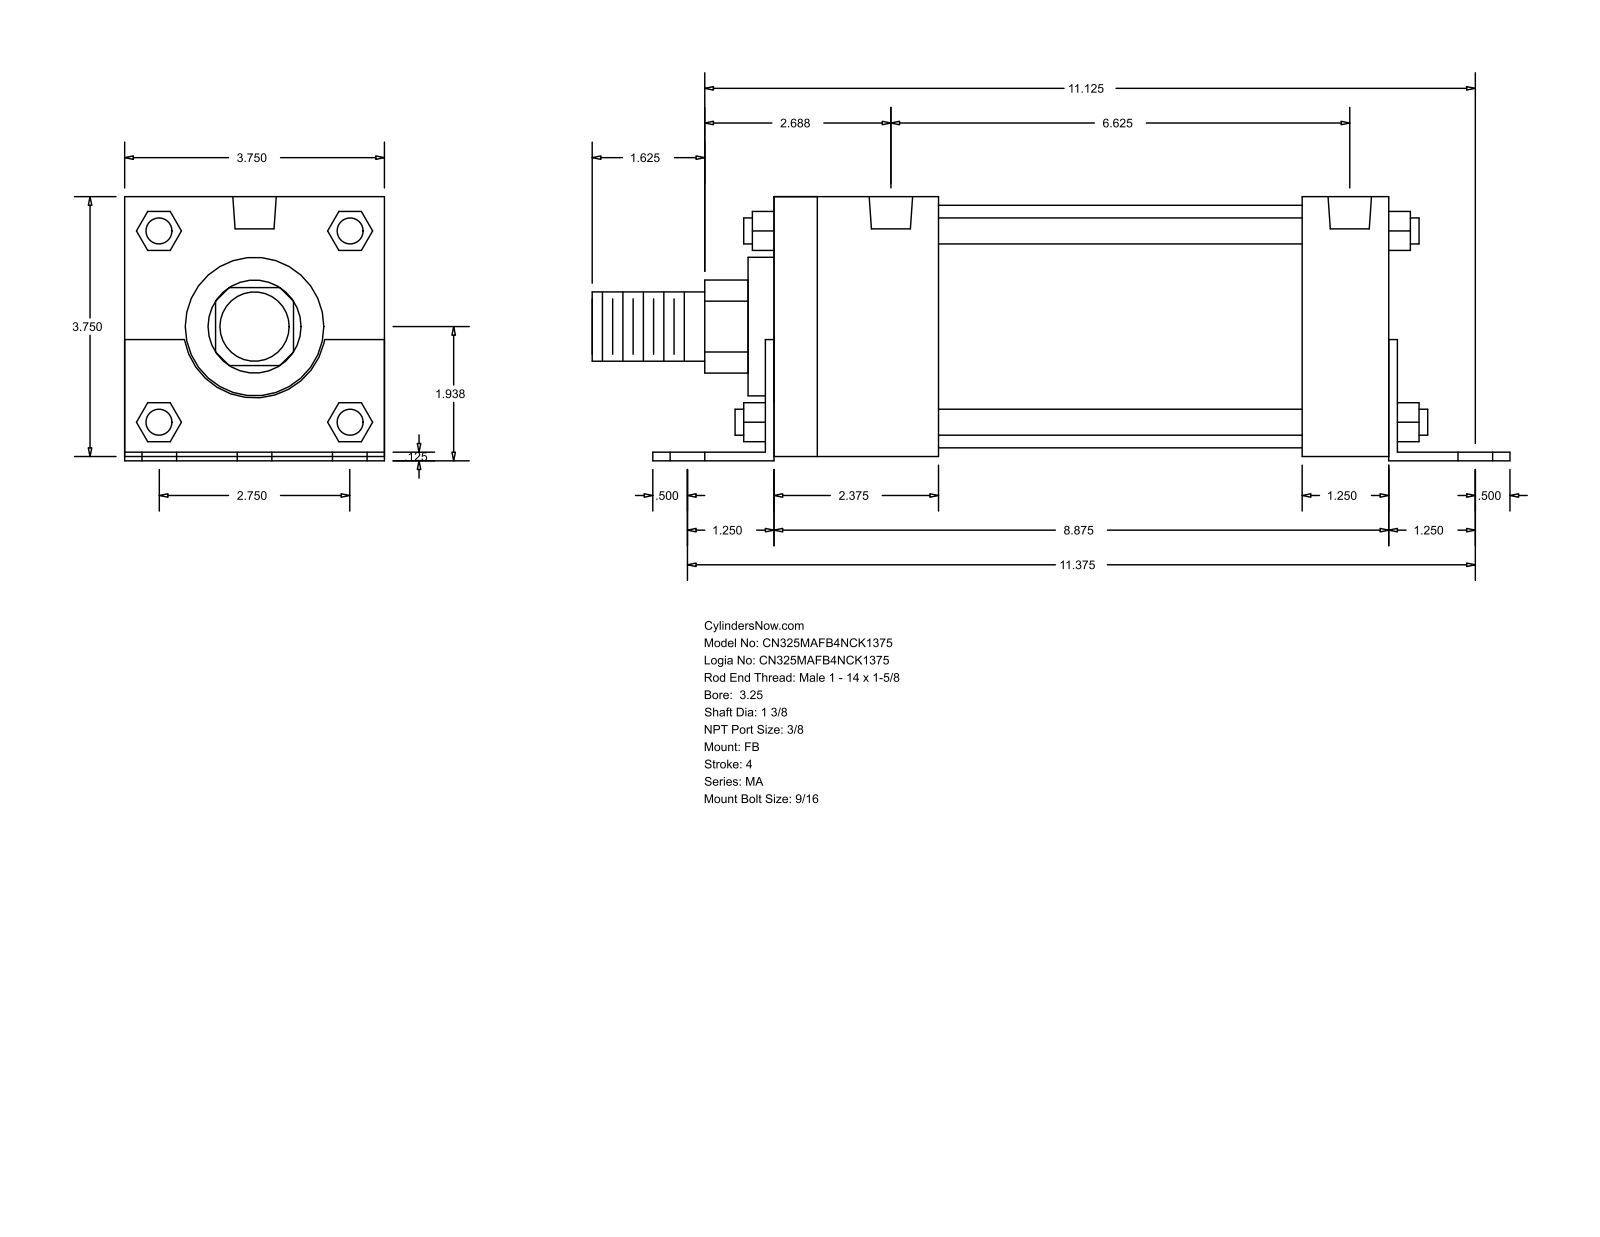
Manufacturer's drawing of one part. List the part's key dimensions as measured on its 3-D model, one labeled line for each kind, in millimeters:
Part name (STEP PRODUCT): MA_FB__0325_1.375
STEP written by: GSSL Pune (CONFIG_CONTROL_DESIGN)
Units: millimetres
Bodies: 0 solids, 140 faces (105 planar, 35 cylindrical, 0 other)
Overall size (bounding box): 336.55 × 96.84 × 95.25
Round holes (diameter × count): ⌀14.29 ×6, ⌀11.11 ×4, ⌀15.93 ×2
Round bosses / shafts (diameter × count): ⌀9.53 ×4, ⌀88.9 ×1, ⌀50.8 ×1, ⌀34.92 ×1, ⌀25.4 ×1
Partial cylindrical surfaces — rounded edges, fillets, slot ends (radius × count): R17.06 ×1, R26.16 ×1
Main face-to-face distances: 95.24, 3.17, 1.59, 96.83, 1.58, 93.66, 3.18, 225.42, 228.6, 31.75
Hole centre spacings: 34.92, 291.02, 288.92, 57.78, 61.64, 69.84, 82.38, 86.72
